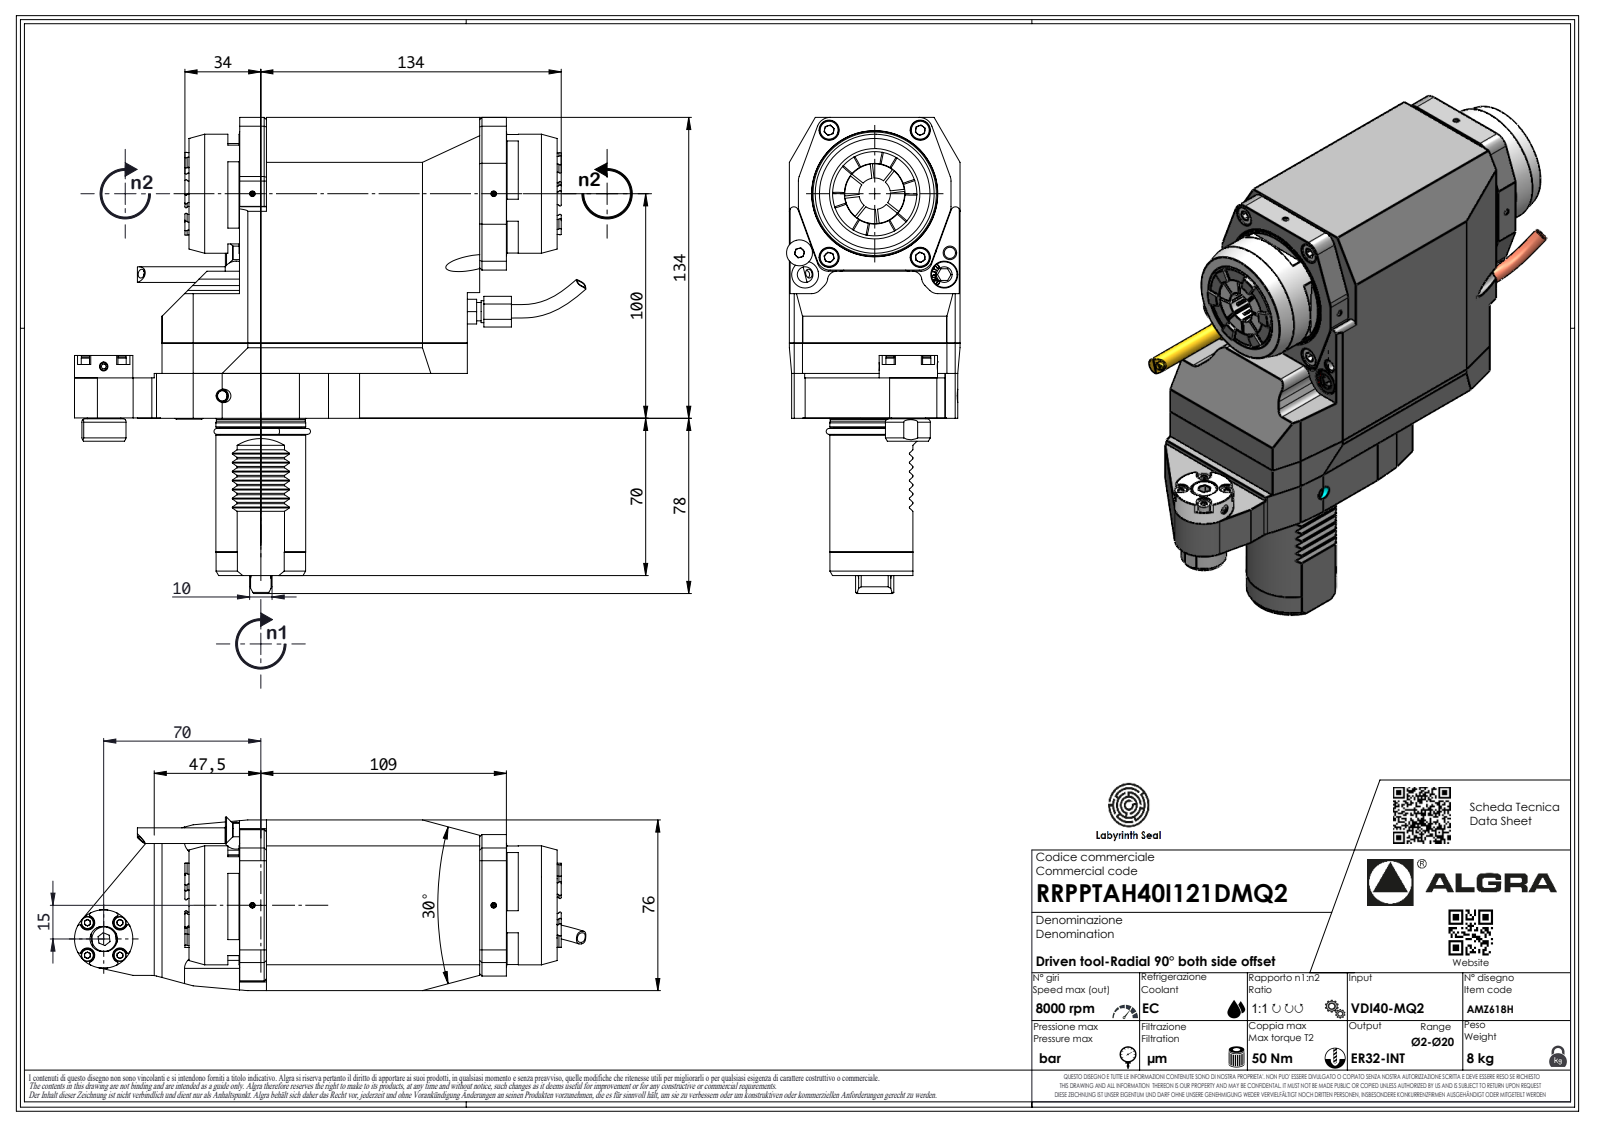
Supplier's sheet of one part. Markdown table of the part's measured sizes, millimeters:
| quantity | value |
| --- | --- |
| part name | RRPPTAH40I121DMQ2 |
| STEP written by | SolidWorks 2023 (AUTOMOTIVE_DESIGN) |
| units | millimeters |
| bodies | 1 solid, 603 faces (428 planar, 79 cylindrical, 96 other) |
| overall size | 227.81 × 212 × 76 |
| volume | 1 355 000 mm³ |
| surface area | 96 048 mm² |
| round holes (diameter × count) | 2.1 × 1, 4 × 1 |
| round bosses / shafts (diameter × count) | 53 × 1, 40 × 1, 39.9 × 1, 39.6 × 1, 36 × 1, 26 × 1, 20 × 1, 15 × 1 |
| partial cylindrical surfaces (radius × count) | 6 × 10, 0.3 × 7, 0.33 × 7, 0.52 × 7, 3.7 × 7, 5 × 6, 2 × 3, 4 × 2 |
| main face-to-face distances | 76, 134, 20, 114, 88, 22.6, 141.4, 136, 12, 34.5 |
